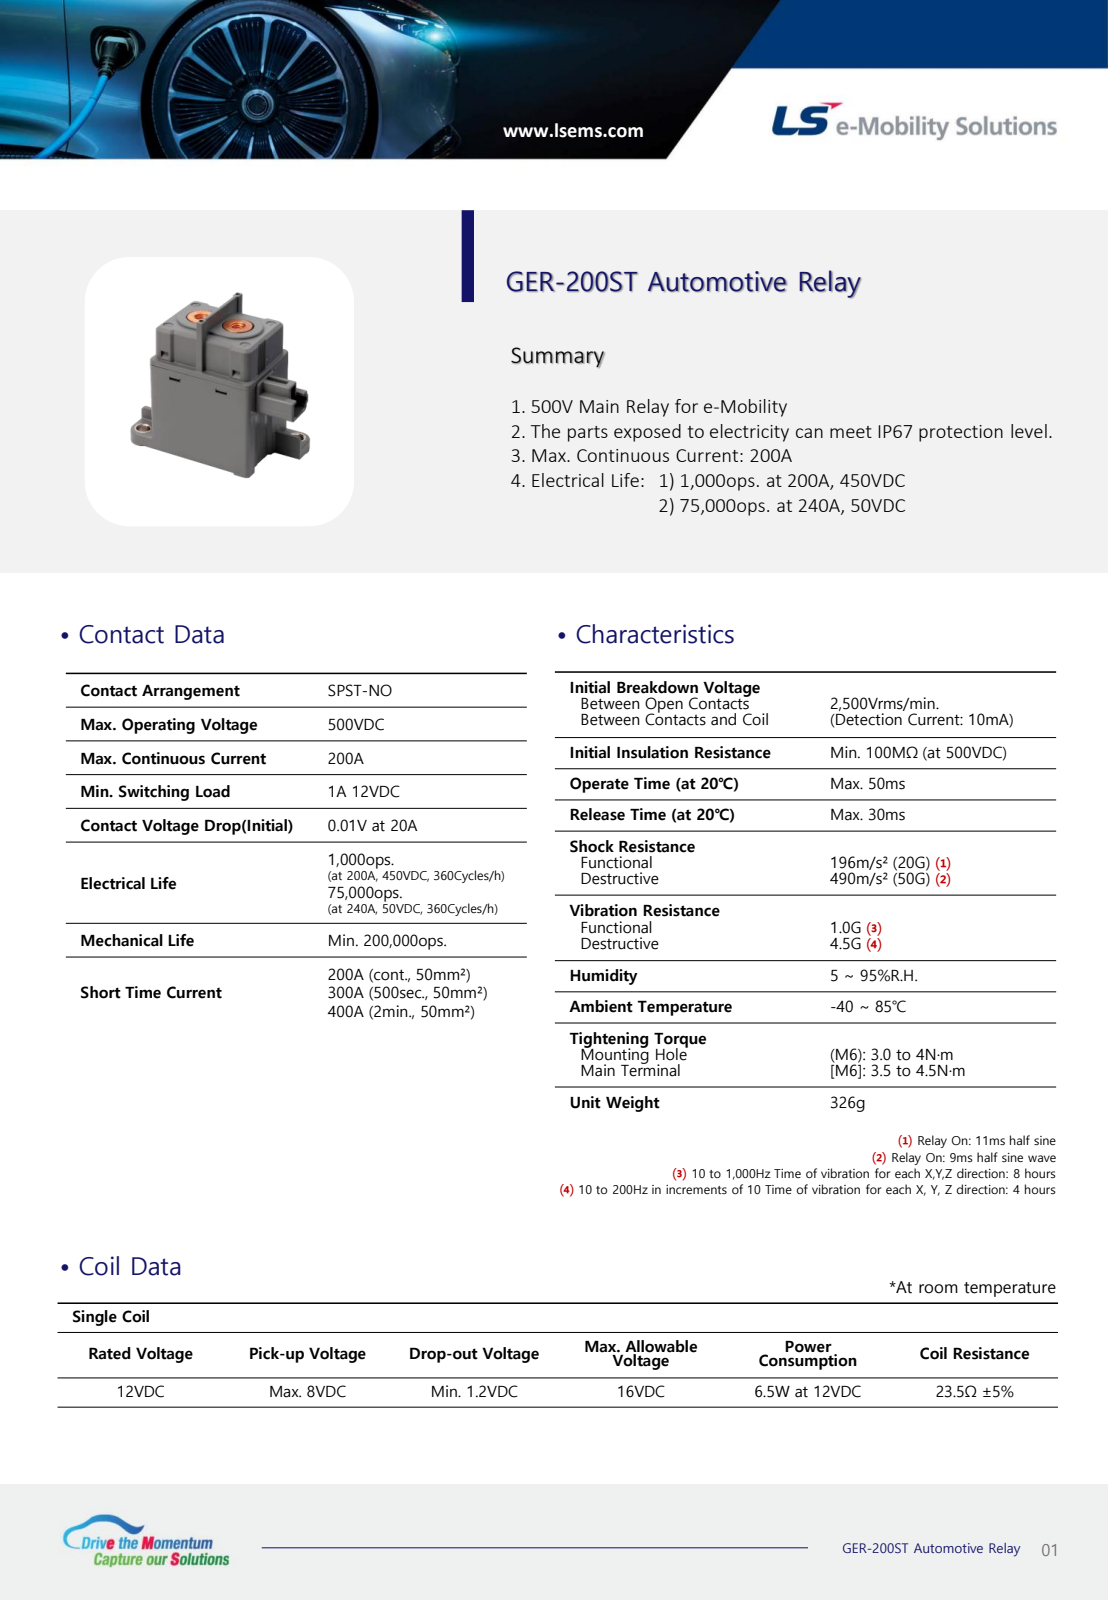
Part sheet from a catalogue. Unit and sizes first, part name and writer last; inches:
Units: inches
Overall size (bounding box): 3.175 × 2.756 × 1.535
Round holes (diameter × count): ⌀0.177 ×4, ⌀0.236 ×4, ⌀0.244 ×2, ⌀0.291 ×2, ⌀0.331 ×2, ⌀0.409 ×2, ⌀0.543 ×2, ⌀0.551 ×1
Round bosses / shafts (diameter × count): ⌀0.118 ×4, ⌀0.638 ×2, ⌀0.512 ×2, ⌀0.472 ×2, ⌀0.457 ×2, ⌀0.335 ×2, ⌀0.276 ×2
Partial cylindrical surfaces — rounded edges, fillets, slot ends (radius × count): R0.02 ×223, R0.039 ×28, R0.047 ×6, R0.079 ×6, R0.094 ×5, R0.024 ×4, R0.118 ×4, R0.004 ×2
Main face-to-face distances: 0.051, 1.484, 0.071, 0.055, 1.535, 1.835, 1.433, 0.059, 0.15, 0.106
Hole centre spacings: 0.615, 0.885, 1.199, 0.354, 0.525, 0.945, 1.059, 1.131
Volume: 1.786 in³ · Surface area: 56.46 in²
Bodies: 9 solids, 1538 faces (662 planar, 472 cylindrical, 404 other)
Part name (STEP PRODUCT): EV-Relay_AllCATPart
STEP written by: CATIA V5 STEP AP214 (AUTOMOTIVE_DESIGN)
